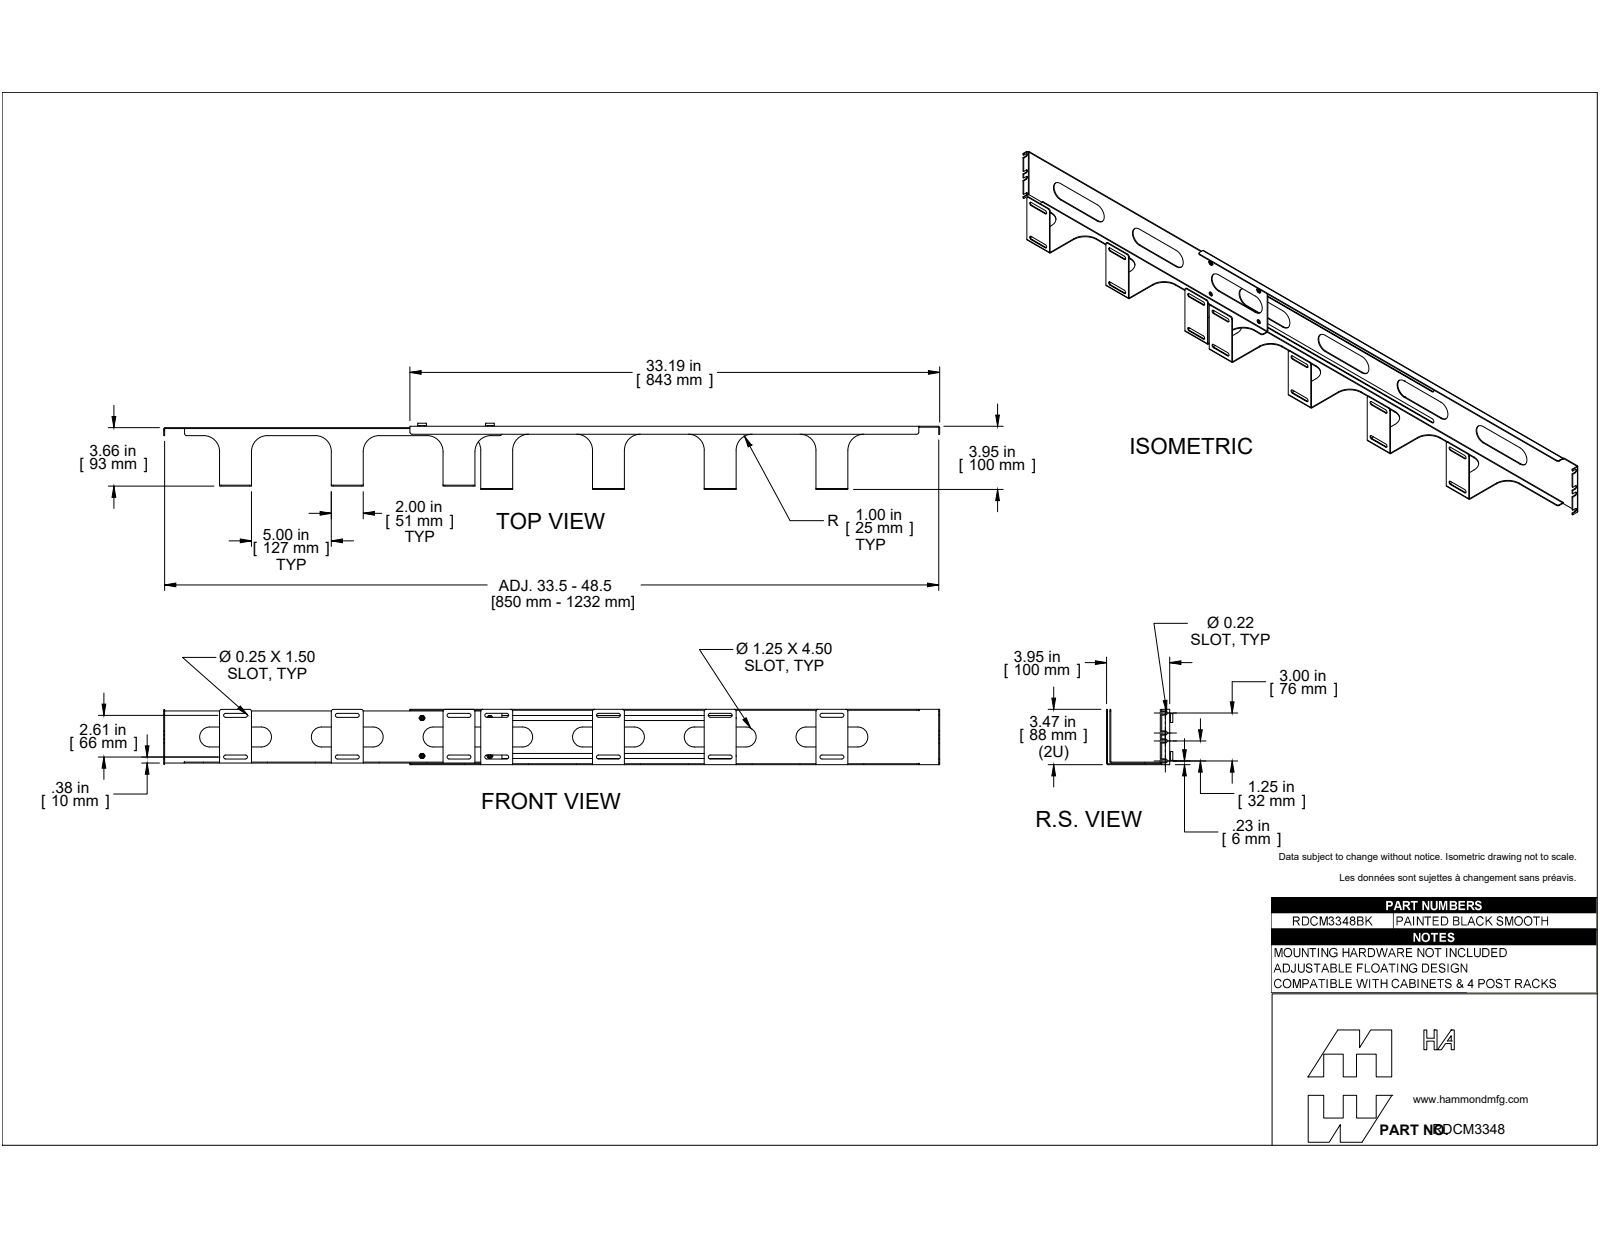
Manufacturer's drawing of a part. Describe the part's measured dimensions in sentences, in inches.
The part is named "RDCM3348BK". Its 3-D file was written by "SolidWorks 2019 (AUTOMOTIVE_DESIGN)". It is 18 solids with 475 faces: 278 planar, 145 cylindrical and 52 other. Overall it measures 48.614 by 4.147 by 3.468 inches. Its volume is 15.15 cubic inches and its surface area 557.4 square inches. Round holes: 4 of diameter 0.159, 4 of diameter 0.281, 4 of diameter 0.313. Round bosses or shafts: 4 of diameter 0.51, 4 of diameter 0.277, 4 of diameter 0.19, 4 of diameter 0.148. Partial cylindrical surfaces (rounded edges, fillets, slot ends): 51 of radius 0.125, 15 of radius 0.625, 14 of radius 1, 7 of radius 0.029, 7 of radius 0.086, 4 of radius 0.109, 4 of radius 0.158, 2 of radius 0.06. The main face-to-face distances are 0.057, 0.087, 0.057, 0.03, 0.144, 3.81, 3.897, 0.104, 0.047, 0.161. The hole center spacings are 2.375, 4.25, 4.869.
